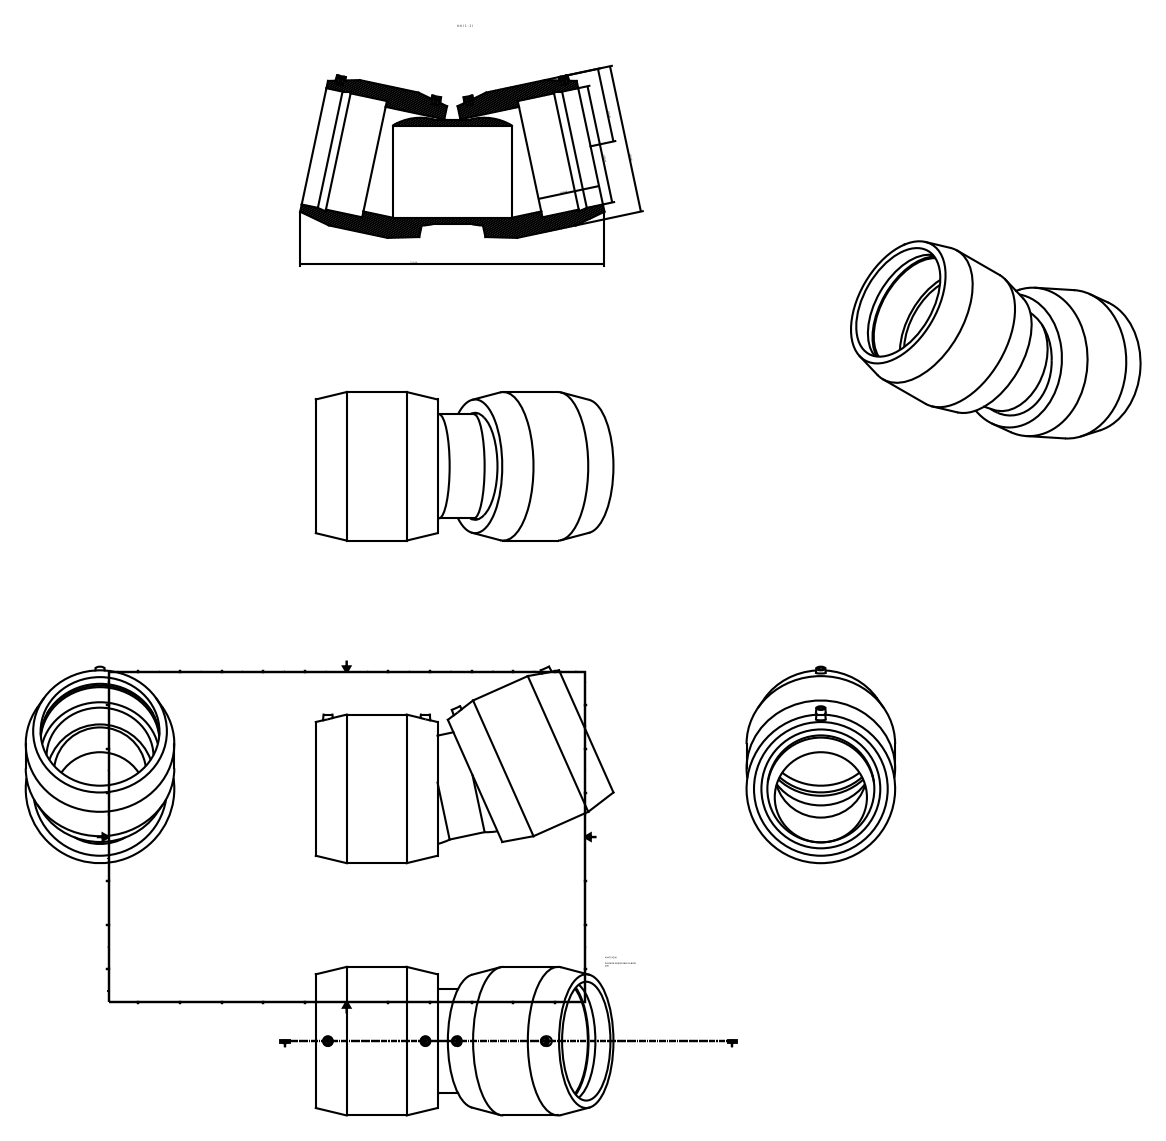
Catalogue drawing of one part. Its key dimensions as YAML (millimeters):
part_name: "4947C4200"
step_written_by: "Autodesk Inventor 2015 (AUTOMOTIVE_DESIGN)"
units: millimeters
bodies: {solids: 1, faces: 50, planar: 20, cylindrical: 18, other: 12}
overall_size: [500.81, 330.64, 250]
volume: 8414000
surface_area: 786909
round_holes:
  - {diameter: 10, count: 4}
  - {diameter: 200, count: 3}
  - {diameter: 180, count: 2}
  - {diameter: 155.11, count: 1}
round_bosses_or_shafts:
  - {diameter: 4, count: 4}
  - {diameter: 250, count: 2}
  - {diameter: 175.27, count: 1}
face_to_face_distances: [204.91, 204.8, 104, 100.8, 100.85, 104.06, 41.6, 62.4, 163.2, 163.29]
hole_center_spacings: [163.84]
